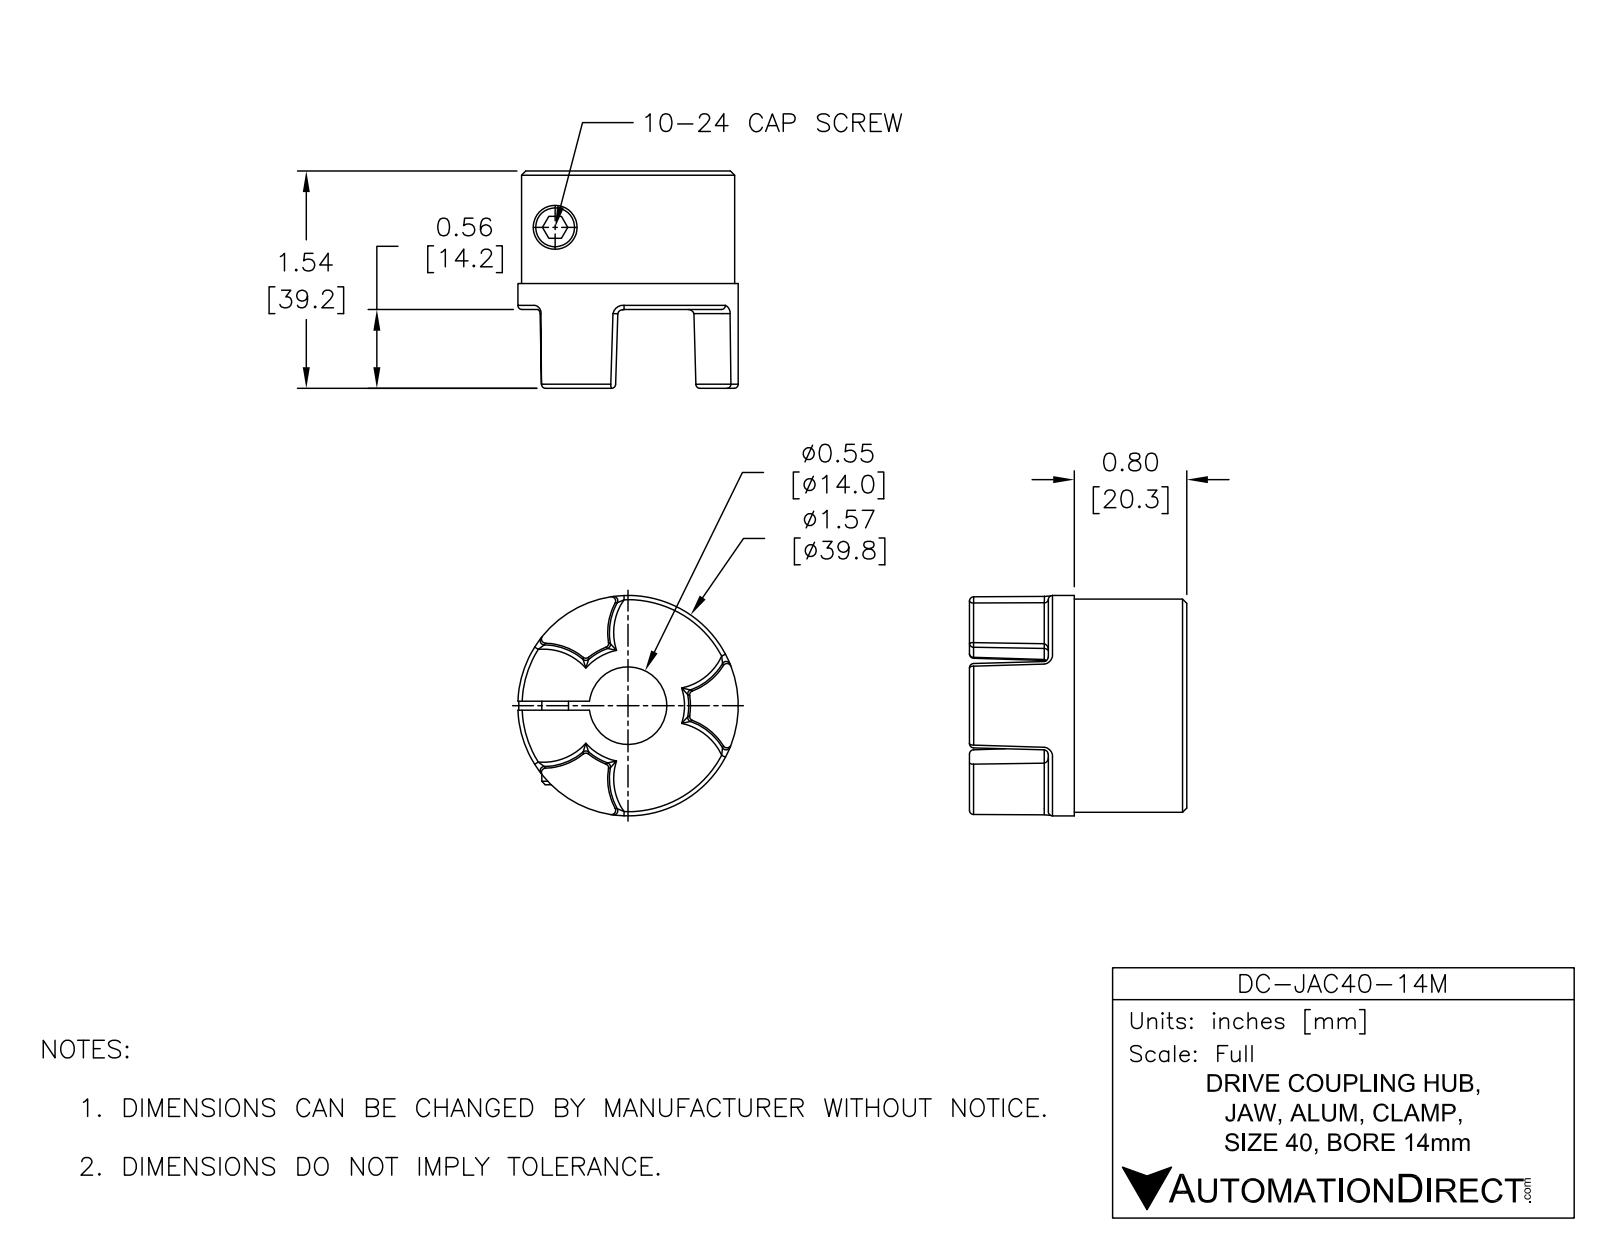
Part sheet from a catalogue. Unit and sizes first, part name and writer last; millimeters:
Units: millimetres
Overall size (bounding box): 39.78 × 39.76 × 39.22
Round holes (diameter × count): ⌀5.11 ×1, ⌀8.36 ×1, ⌀14 ×1
Round bosses / shafts (diameter × count): ⌀39.78 ×1, ⌀38.48 ×1
Partial cylindrical surfaces — rounded edges, fillets, slot ends (radius × count): R0.76 ×2
Main face-to-face distances: 24.99, 1.6, 39.22, 14.23, 20.29, 4.7, 18.93, 3.99, 5.59
Volume: 27 964 mm³ · Surface area: 8 719 mm²
Bodies: 1 solid, 107 faces (12 planar, 17 cylindrical, 78 other)
Part name (STEP PRODUCT): DC-JAC40-14M
STEP written by: SolidWorks 2015 (AUTOMOTIVE_DESIGN)
